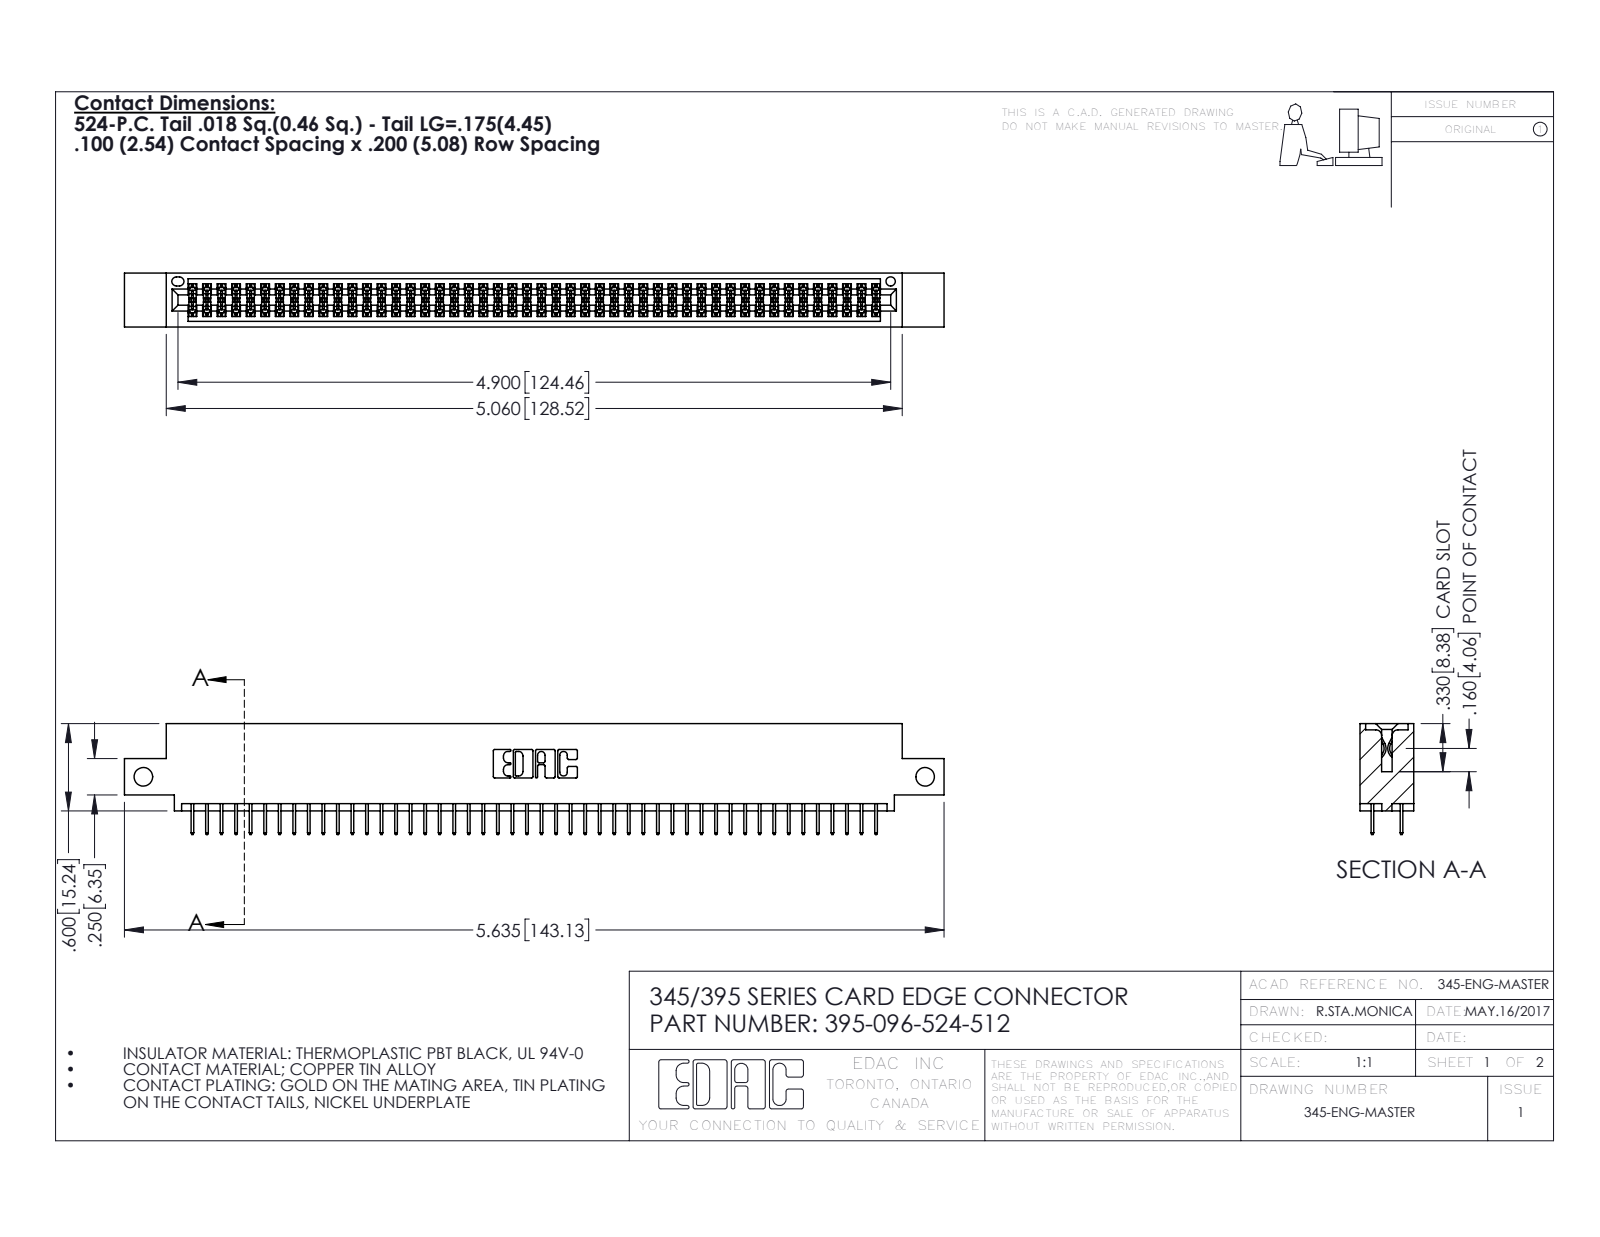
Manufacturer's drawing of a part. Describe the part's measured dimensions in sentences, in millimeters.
The part is named "345 Part_0.110 Offset - Side Mount; 395-096-524-512; 345-292-001_345-293-124". Its 3-D file was written by "SolidWorks 2016 (CONFIG_CONTROL_DESIGN)". It is 97 solids with 5314 faces: 3828 planar, 1486 cylindrical and 0 other. Overall it measures 143.1 by 19.4 by 9.4 millimeters. Its volume is 13 700 cubic millimeters and its surface area 19 870 square millimeters. Round holes: 2 of diameter 3.3, 1 of diameter 1.6. Partial cylindrical surfaces (rounded edges, fillets, slot ends): 144 of radius 0.2, 22 of radius 0.3, 6 of radius 0.2, 6 of radius 0.8, 3 of radius 0.7, 2 of radius 0.4, 2 of radius 0.5, 2 of radius 0.6. The main face-to-face distances are 1.8, 7.6, 5.1, 9.4, 2.5, 6.9, 0.6, 5.7, 1.8, 4.4. The hole center spacings are 136.5.
